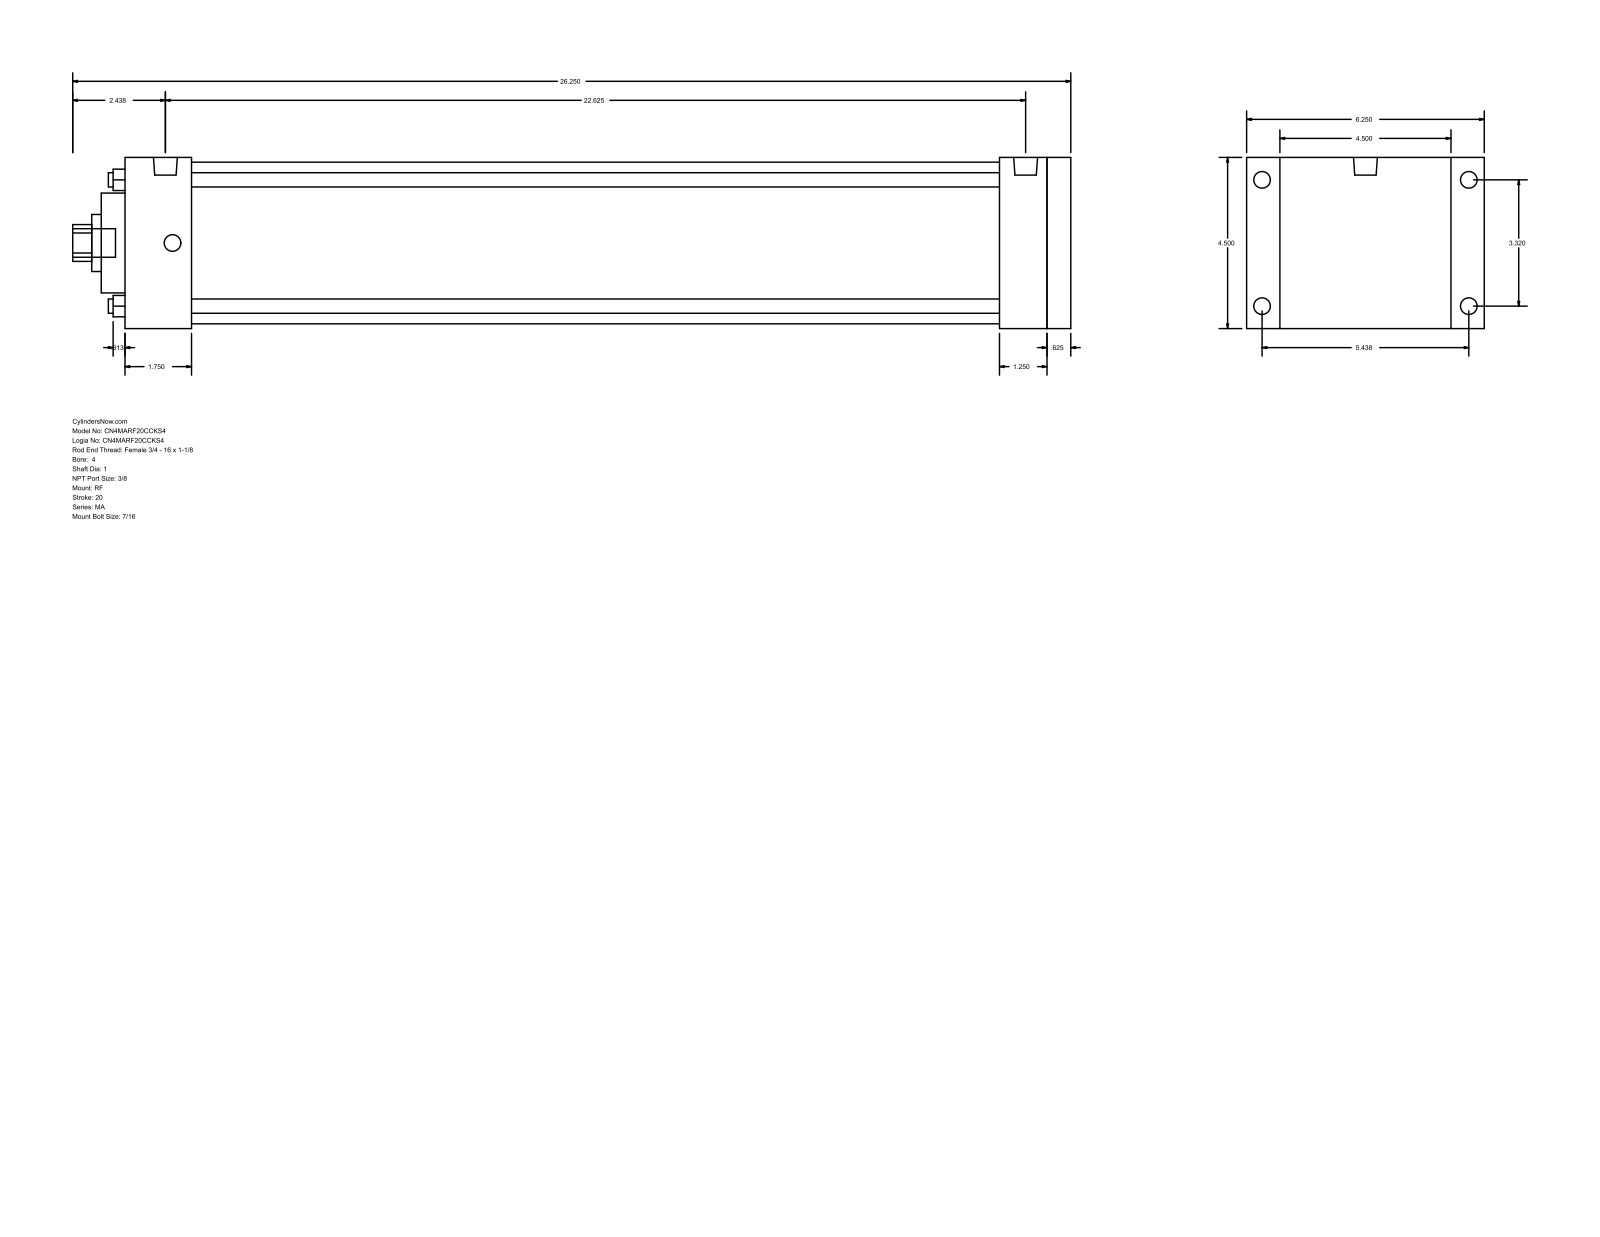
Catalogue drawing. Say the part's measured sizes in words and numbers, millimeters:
The part is named "MA_RF__0400_1". Its 3-D file was written by "GSSL Pune (CONFIG_CONTROL_DESIGN)". It is 0 solids with 94 faces: 65 planar, 29 cylindrical and 0 other. Overall it measures 666.75 by 158.75 by 114.3 millimeters. Round holes: 4 of diameter 9.53, 1 of diameter 25.4, 1 of diameter 38.1, 1 of diameter 66.67, 1 of diameter 107.95. Round bosses or shafts: 8 of diameter 11.11, 2 of diameter 15.93, 1 of diameter 19.05. Partial cylindrical surfaces (rounded edges, fillets, slot ends): 1 of radius 12.29. The main face-to-face distances are 114.3, 631.83, 15.87, 615.96, 22.23, 136.53, 584.2, 31.76, 47.63, 44.46. The hole center spacings are 59.62, 84.32, 119.25.
